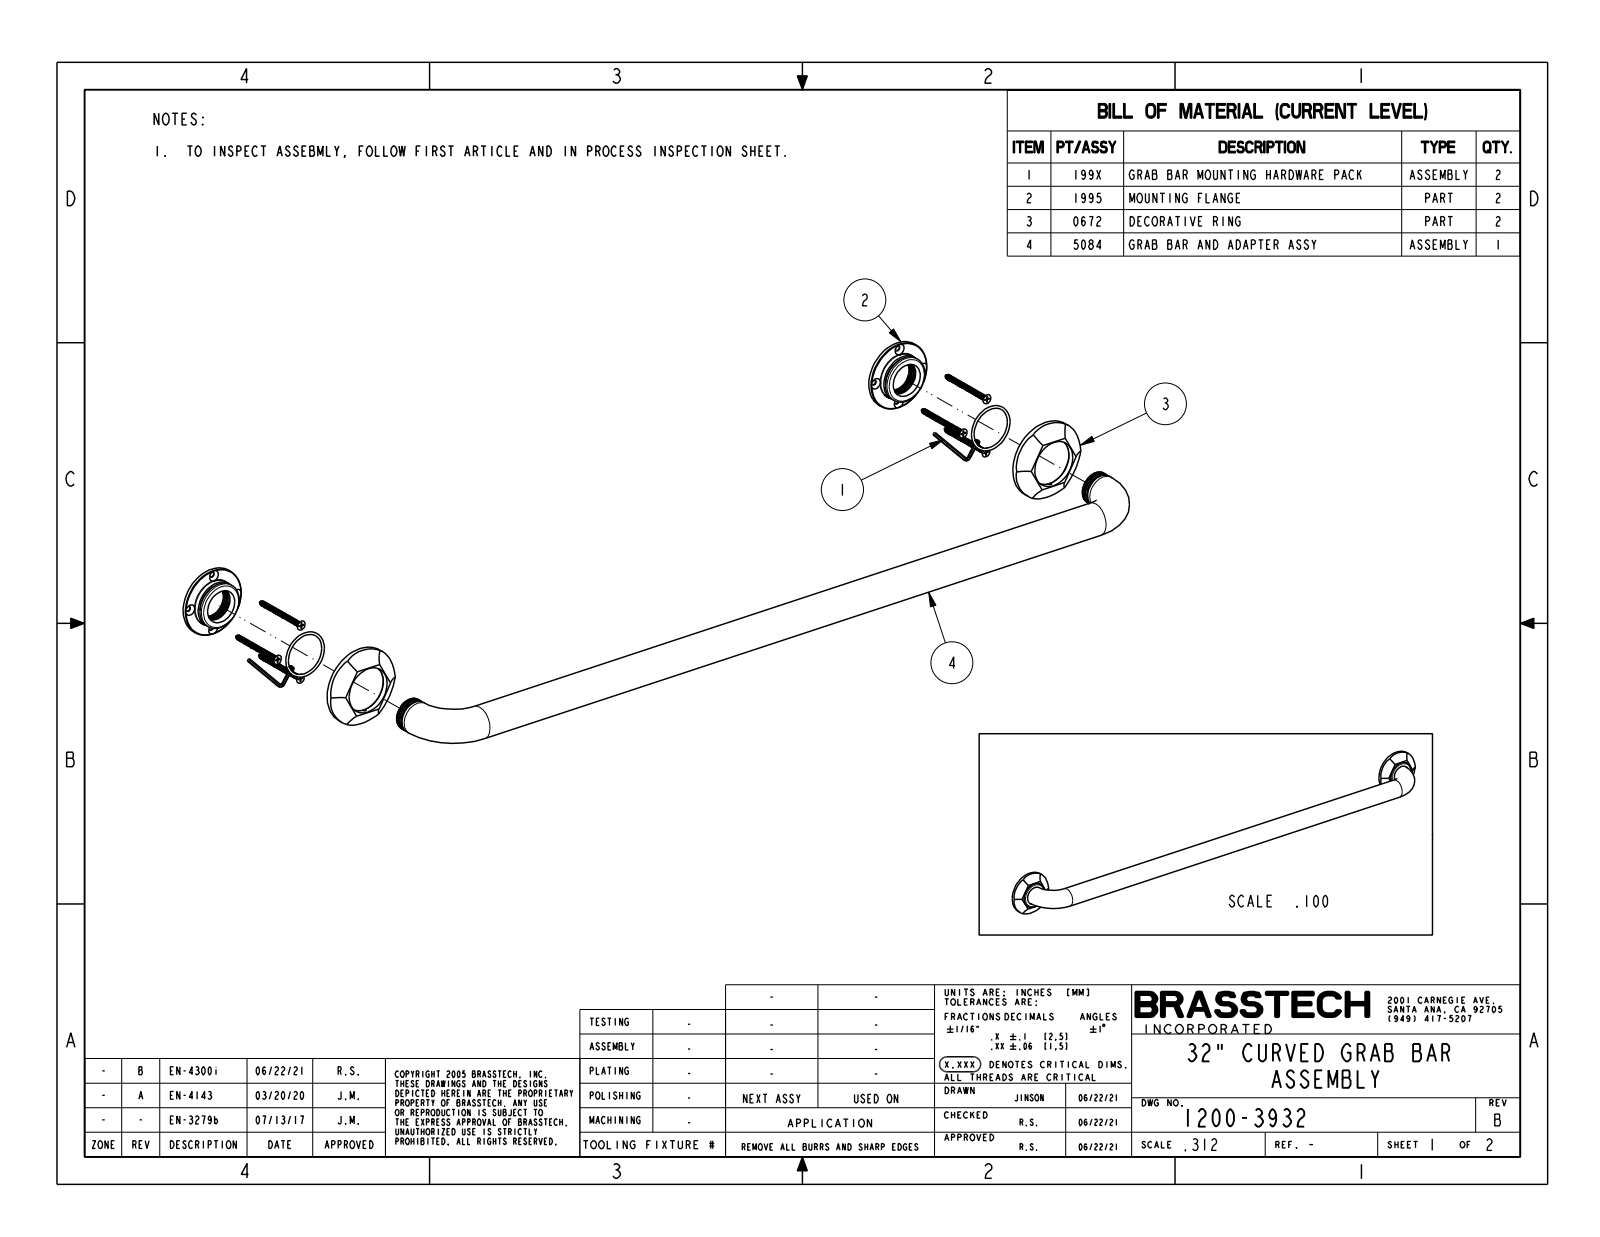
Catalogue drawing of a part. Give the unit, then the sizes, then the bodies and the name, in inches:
Units: inches
Overall size (bounding box): 35 × 3 × 2.75
Round bosses / shafts (diameter × count): ⌀3 ×2, ⌀1.75 ×2, ⌀1.25 ×1
Partial cylindrical surfaces — rounded edges, fillets, slot ends (radius × count): R1.181 ×10
Main face-to-face distances: 0.6, 0.525, 0.075
Volume: 47.2 in³ · Surface area: 163.5 in²
Bodies: 1 solid, 36 faces (6 planar, 22 cylindrical, 8 other)
Part name (STEP PRODUCT): 1200-3932_SW0001
STEP written by: CREO PARAMETRIC BY PTC INC, 2018400 (CONFIG_CONTROL_DESIGN)
